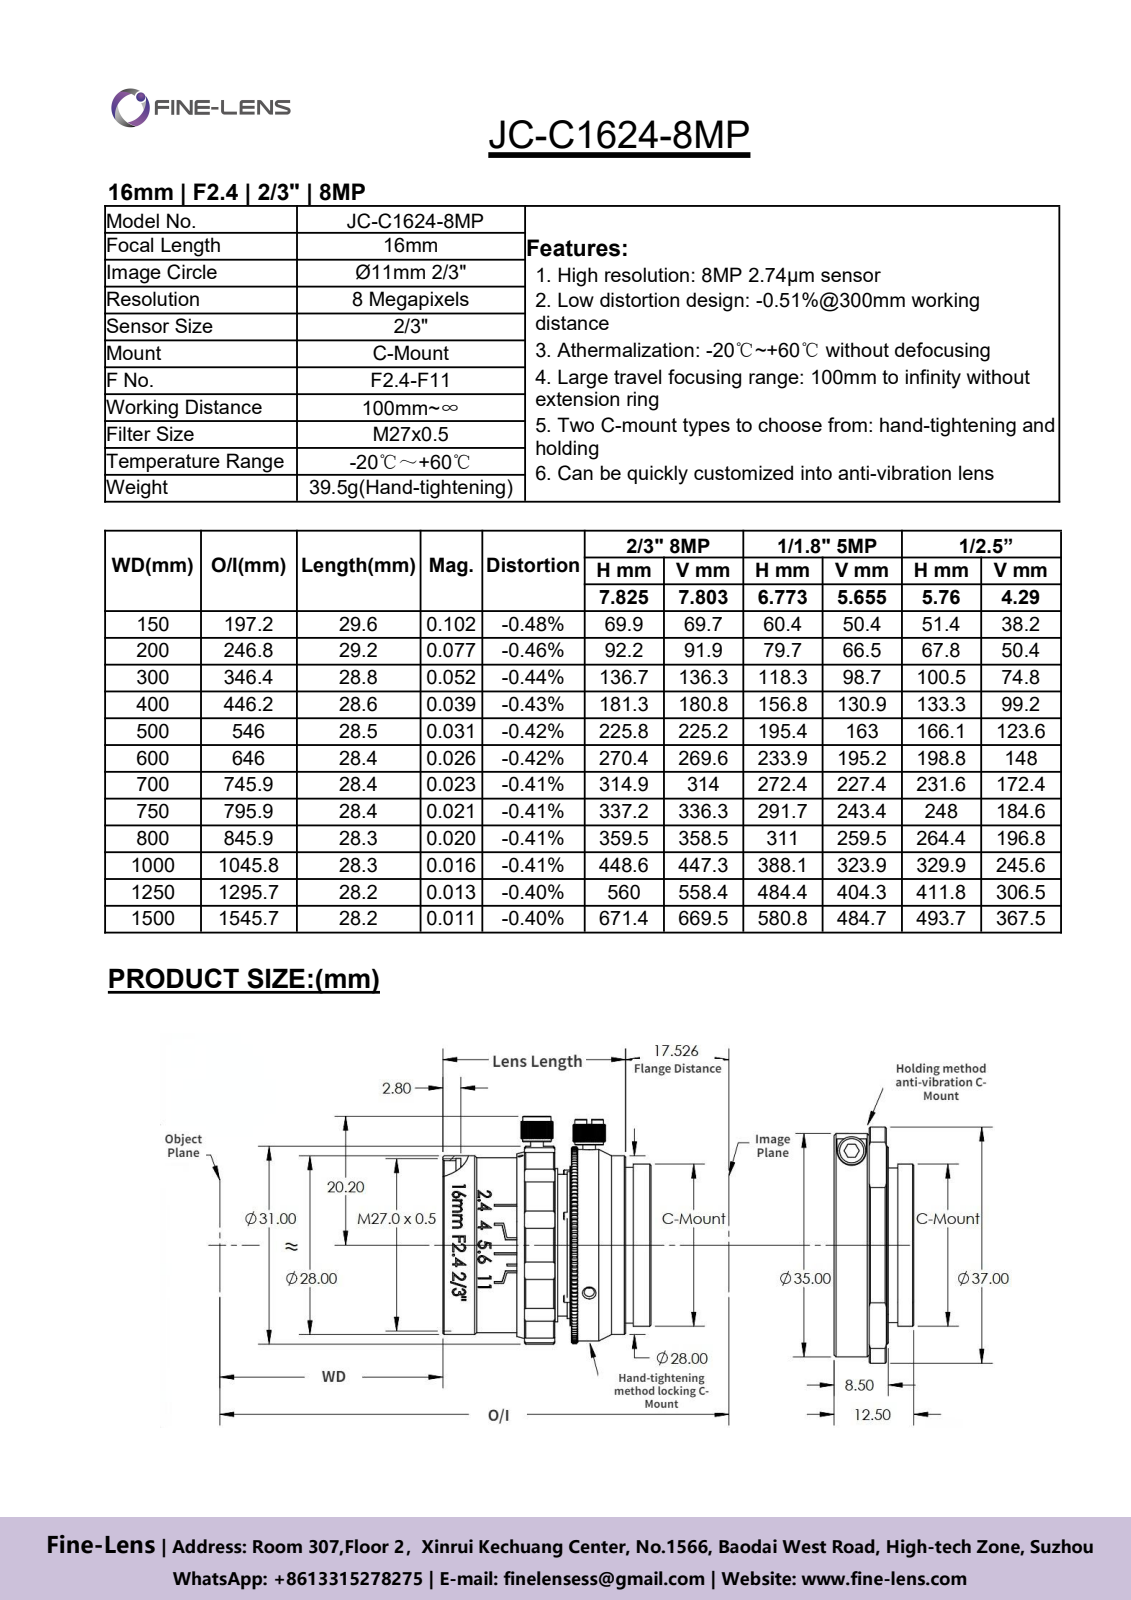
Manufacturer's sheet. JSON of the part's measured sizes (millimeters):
{"step_written_by": "SolidWorks 2018 (CONFIG_CONTROL_DESIGN)", "units": "millimeters", "bodies": {"solids": 3, "faces": 1121, "planar": 418, "cylindrical": 248, "other": 455}, "overall_size": [32.32, 31, 31], "volume_mm3": 17381, "surface_area_mm2": 8646, "round_holes": [[1.6, 4], [0.5, 1], [18, 1], [19.2, 1], [19.6, 1], [22.4, 1], [24.2, 1], [26.5, 1], [27.6, 1], [29, 1]], "round_bosses_or_shafts": [[30, 1], [28, 1], [27.4, 1], [25.4, 1], [24.4, 1], [24, 1], [23.2, 1], [23, 1]], "partial_cylinders_radius": [[2.5, 12], [1, 1], [13.75, 1], [14.05, 1], [15.4, 1], [15.5, 1]], "face_to_face_distances": [8.38, 17.77, 26.15, 10.25, 7.52, 15.9, 14.5, 4.25, 3.27, 11.65]}
